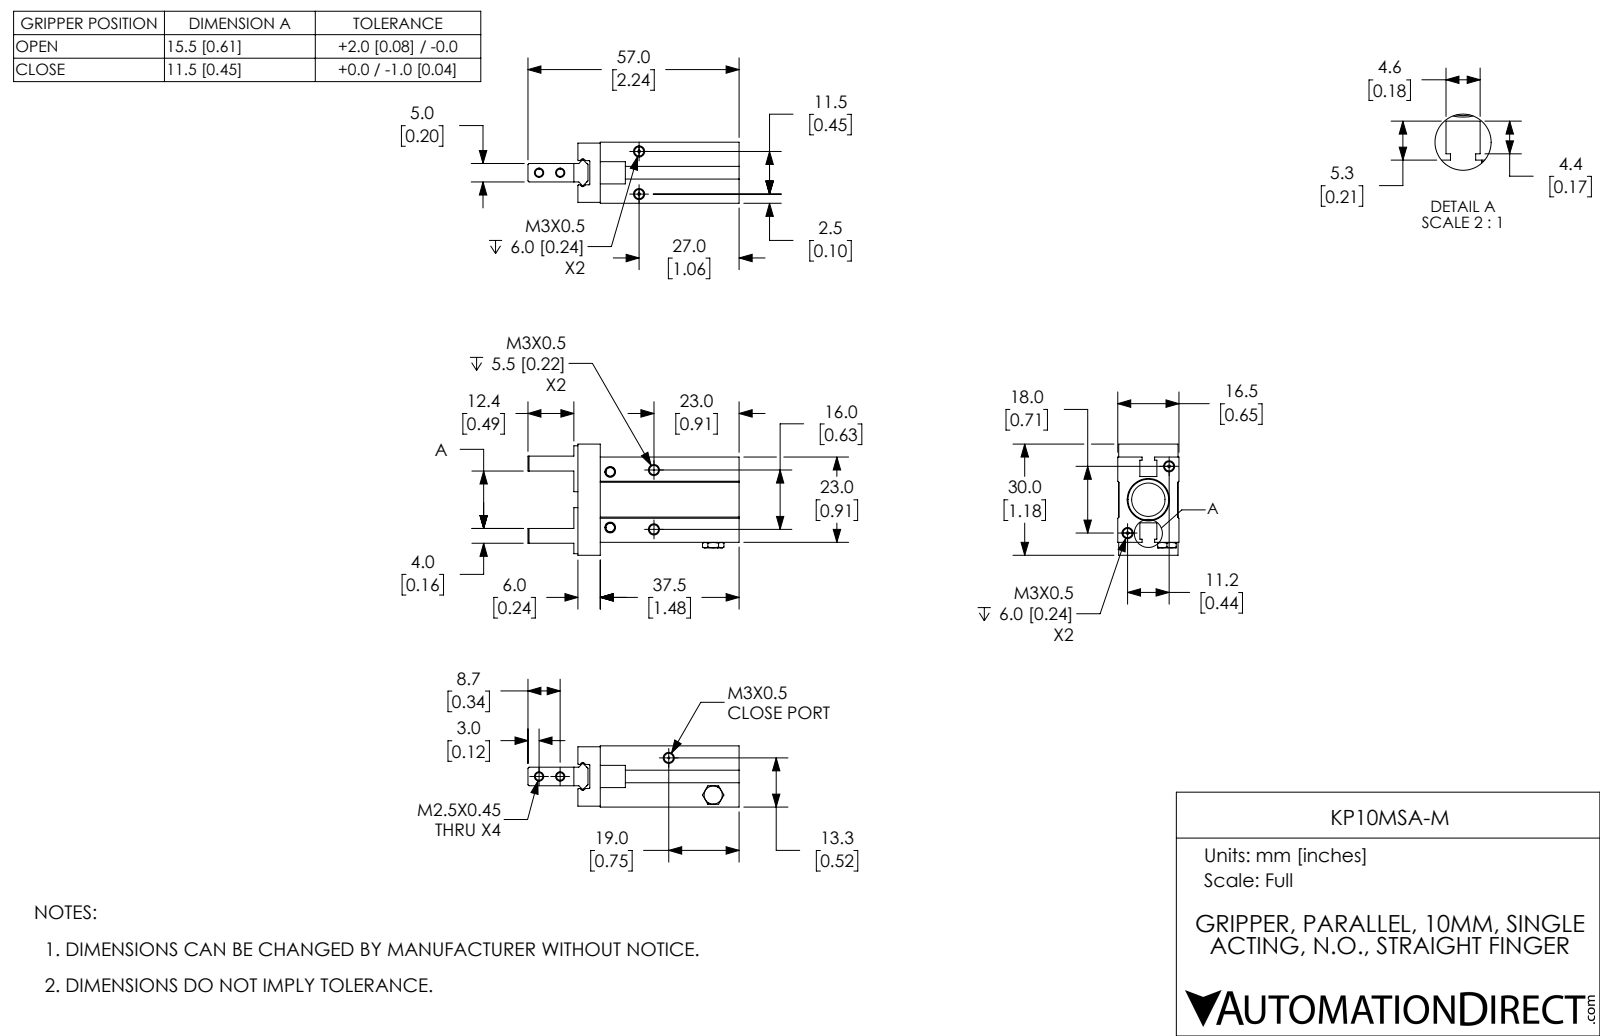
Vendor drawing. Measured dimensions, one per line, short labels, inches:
name: KP10MSA-M; KP10MSA-M-3; KP10MSA-M-2; KP10MSA-M-1
written by: SolidWorks 2017 (CONFIG_CONTROL_DESIGN)
unit: in
bodies: 3 solids, 240 faces (118 planar, 56 cylindrical, 66 other)
size: 2.244 × 1.181 × 0.65
volume: 0.877 in³; area: 11.61 in²
holes: 4× ⌀0.097, 4× ⌀0.097, 2× ⌀0.02, 2× ⌀0.079, 2× ⌀0.119, 1× ⌀0.354, 1× ⌀0.433
rounds: 4× R0.008, 2× R0.01, 2× R0.03
face distances: 0.638, 0.217, 0.207, 0.197, 0.222, 0.234, 0.415, 0.404, 0.65, 0.906
hole spacings: 0.417, 0.869, 1.087, 0.224, 0.317, 0.453, 0.528, 0.615
